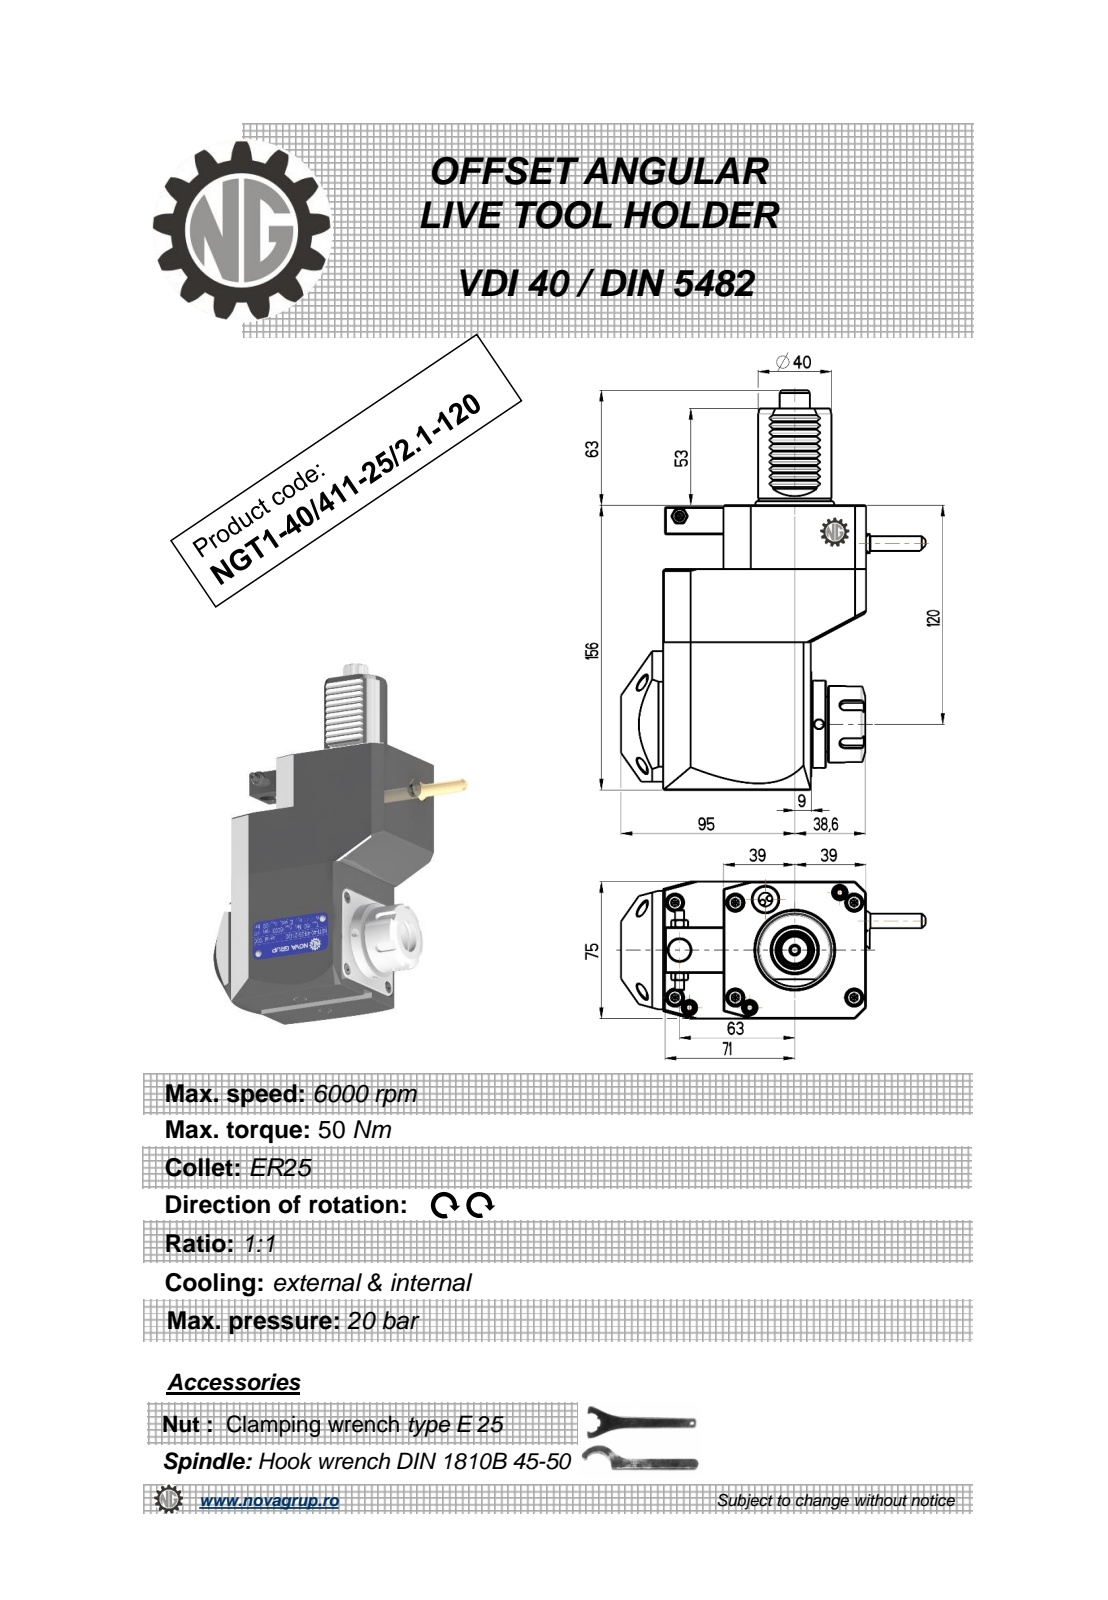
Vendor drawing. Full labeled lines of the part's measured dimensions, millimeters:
Part name (STEP PRODUCT): NGT1_40_411_25_2_1_120
STEP written by: PRO/ENGINEER BY PARAMETRIC TECHNOLOGY CORPORATION, 2010280 (CONFIG_CONTROL_DESIGN)
Units: millimetres
Bodies: 1 solid, 492 faces (202 planar, 124 cylindrical, 166 other)
Overall size (bounding box): 219 × 166.5 × 76.6
Volume: 1 176 000 mm³ · Surface area: 87 050 mm²
Round holes (diameter × count): ⌀5 ×3, ⌀4.2 ×2, ⌀3 ×1, ⌀9.5 ×1, ⌀12 ×1, ⌀20.3 ×1
Round bosses / shafts (diameter × count): ⌀48 ×1, ⌀42 ×1, ⌀40 ×1, ⌀37.5 ×1, ⌀33 ×1, ⌀11.2 ×1, ⌀8.96 ×1, ⌀8 ×1
Partial cylindrical surfaces — rounded edges, fillets, slot ends (radius × count): R3.03 ×18, R0.26 ×12, R0.3 ×10, R0.22 ×6, R3 ×5, R0.5 ×1, R6.75 ×1, R8.22 ×1
Main face-to-face distances: 75, 156, 111, 35, 121, 81, 30, 33, 48, 78
Hole centre spacings: 13.25, 20.93, 63, 76.25, 100.28, 112.5, 137.15
